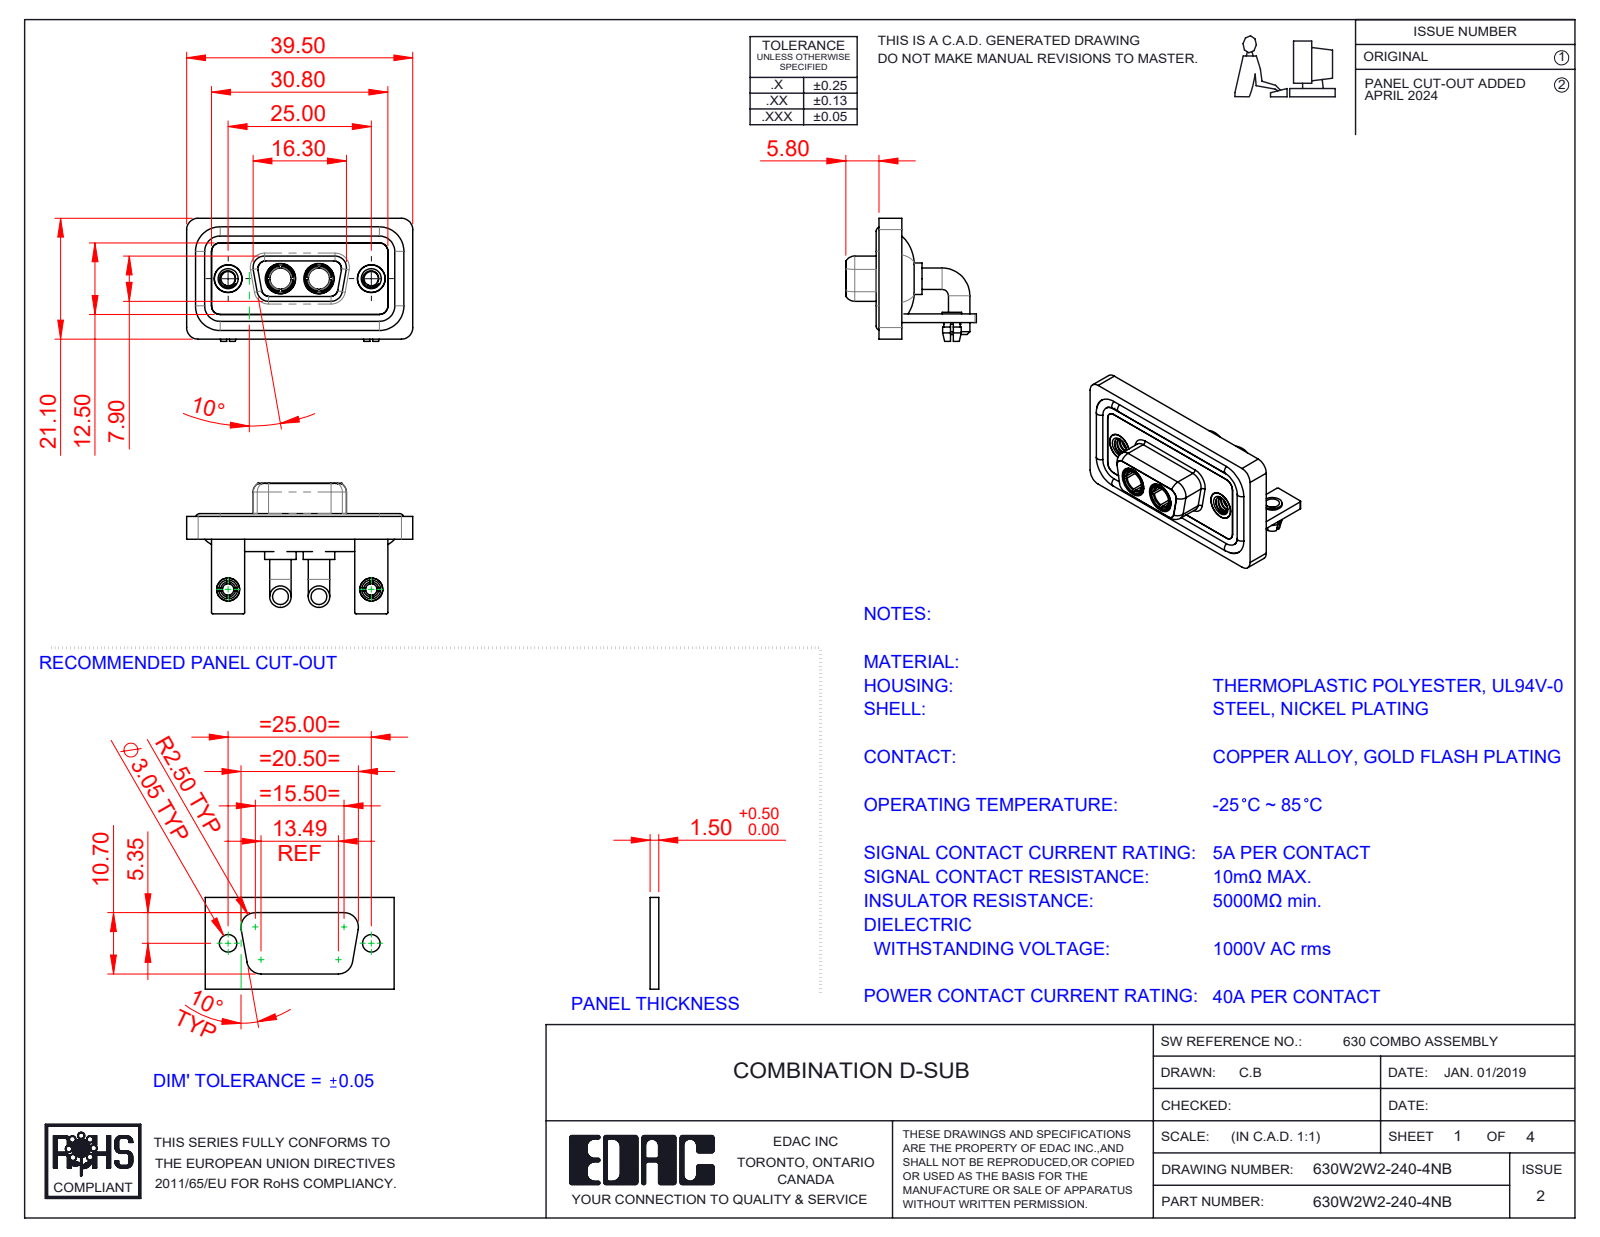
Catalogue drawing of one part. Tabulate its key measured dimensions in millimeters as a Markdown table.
| quantity | value |
| --- | --- |
| part name | 630Combo Stabilizer Bracket_50 Contacts; 630Combo Shell Rear_09 Contacts; 630Combo Housing_2W2; 630Combo Shell Front_09 Contacts (+5 more) |
| STEP written by | SolidWorks 2023 (CONFIG_CONTROL_DESIGN) |
| units | millimeters |
| bodies | 15 solids, 676 faces (231 planar, 292 cylindrical, 153 other) |
| overall size | 39.5 × 22.8 × 21.5 |
| volume | 5 357 mm³ |
| surface area | 8 822 mm² |
| round holes (diameter × count) | 2.5 × 4, 4.85 × 4, 2 × 2, 3.2 × 2, 3.7 × 2, 4 × 2, 4.05 × 2, 5 × 2, 5.3 × 2 |
| round bosses / shafts (diameter × count) | 3.75 × 4, 1.6 × 4, 5.5 × 2, 5.2 × 2, 4.96 × 2, 4.95 × 2, 4.8 × 2, 4.75 × 2 |
| partial cylindrical surfaces (radius × count) | 2 × 19, 1.5 × 18, 0.25 × 16, 1.35 × 8, 1.6 × 8, 0.5 × 5, 0.6 × 4, 0.65 × 4 |
| main face-to-face distances | 0.4, 2.9, 1.5, 1.8, 1.1, 3.7, 0.8, 2.5, 1.6, 3.1 |
| hole center spacings | 9.14, 15.86, 25, 6.72 |
